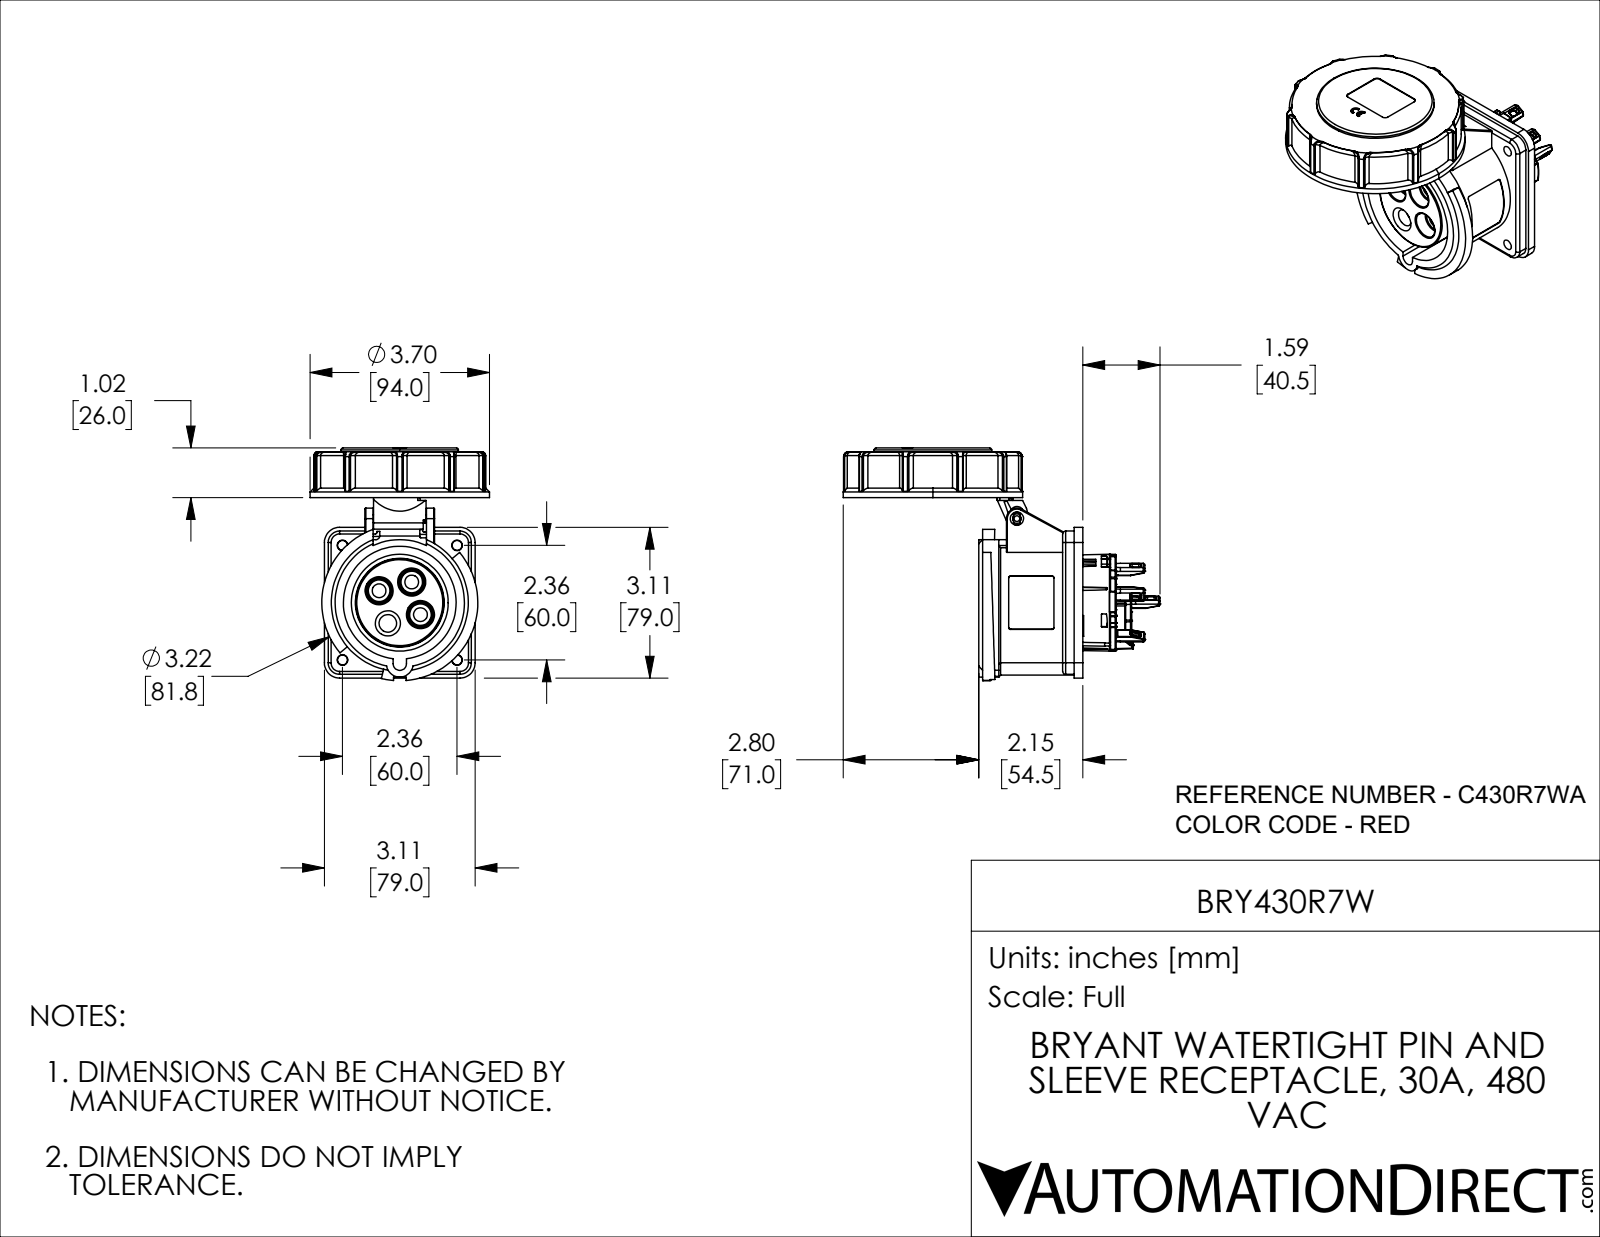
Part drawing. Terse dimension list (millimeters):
name: BRY430R7W
written by: SolidWorks 2021 (CONFIG_CONTROL_DESIGN)
unit: mm
bodies: 4 solids, 2040 faces (588 planar, 805 cylindrical, 647 other)
size: 166 × 121.95 × 94
volume: 345 947 mm³; area: 96 890 mm²
holes: 4× ⌀4.2, 4× ⌀5.2, 4× ⌀5.5, 3× ⌀7.2, 1× ⌀3, 1× ⌀4.3, 1× ⌀7, 1× ⌀9.2, 1× ⌀50.7, 1× ⌀59.1, 1× ⌀65, 1× ⌀84
bosses: 1× ⌀94, 1× ⌀71.75, 1× ⌀64, 1× ⌀61.5, 1× ⌀53, 1× ⌀4
rounds: 93× R0.5, 77× R0.25, 28× R1, 27× R2.5, 24× R0.8, 12× R0.21, 9× R0.3, 8× R0.48
face distances: 2, 4.5, 21, 10.5, 2.5, 6, 50, 8, 3, 23
hole spacings: 12.5, 17.68, 24.87, 30.52, 41.01, 42.43, 47.24, 54.6
